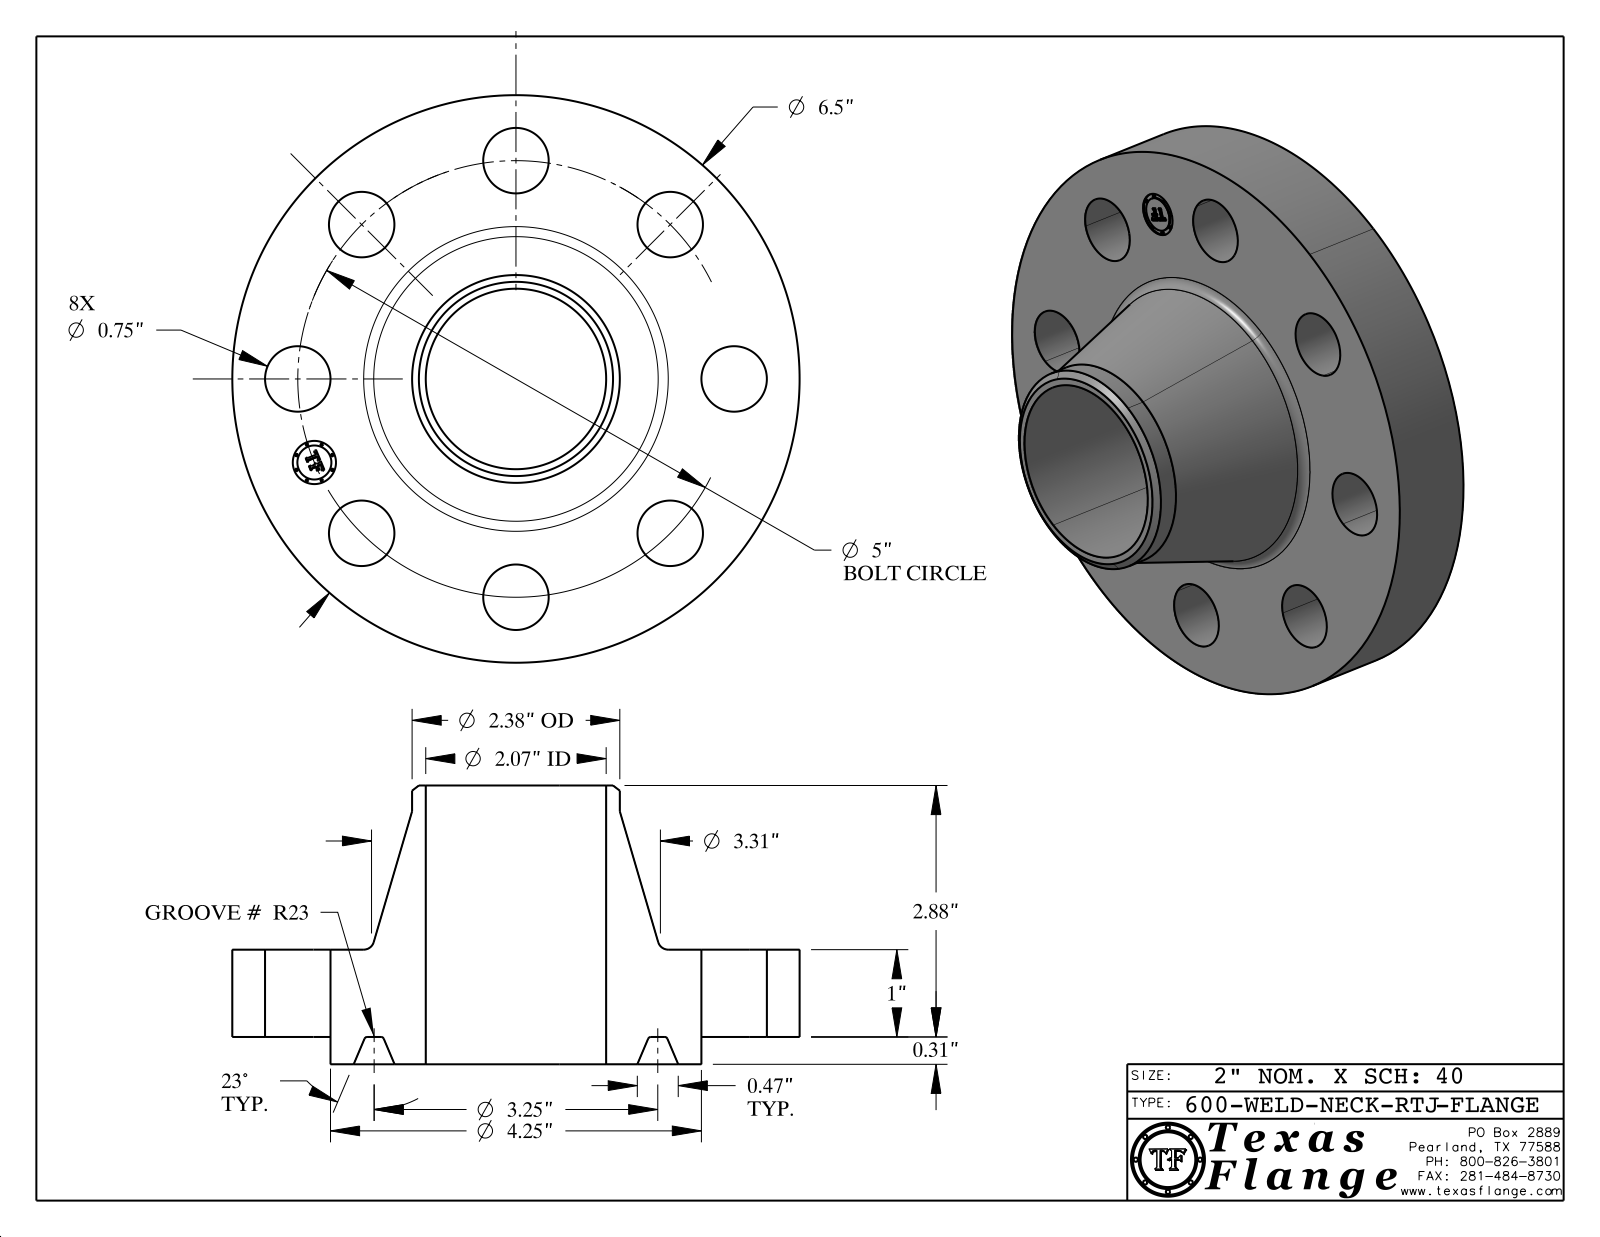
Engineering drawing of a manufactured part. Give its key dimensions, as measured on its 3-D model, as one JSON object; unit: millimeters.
{"part_name": "600-WELD-NECK-RTJ", "step_written_by": "CATIA V5 STEP AP214 (AUTOMOTIVE_DESIGN)", "units": "millimeters", "bodies": {"solids": 1, "faces": 429, "planar": 371, "cylindrical": 44, "other": 14}, "overall_size": [165.1, 165.1, 81.1], "volume_mm3": 553600, "surface_area_mm2": 85940, "round_holes": [[19.1, 8], [12.6, 1], [52.5, 1]], "round_bosses_or_shafts": [[0.8, 8], [165.1, 1], [108, 1], [60.5, 1], [9.9, 1]], "face_to_face_distances": [25.4, 8, 33.4, 81.1, 73.2, 47.8, 33, 25, 0.4, 48.1], "hole_center_spacings": [63.5, 48.6, 89.8, 117.3, 127, 24.8, 70.6, 105.6]}
